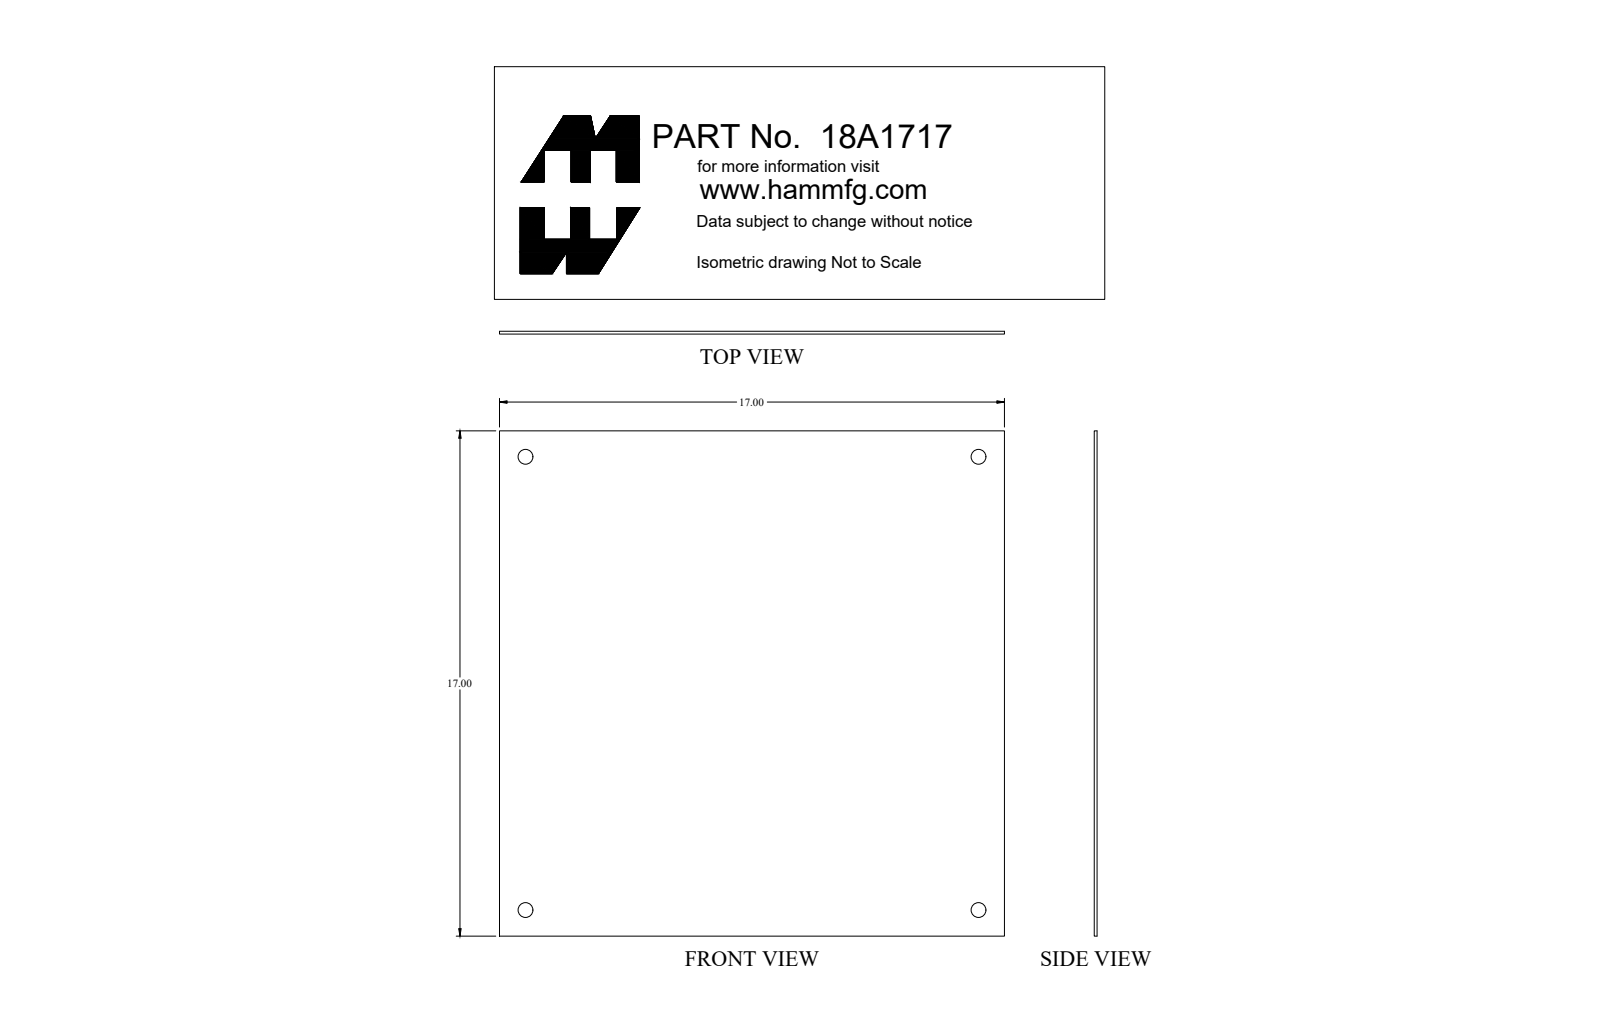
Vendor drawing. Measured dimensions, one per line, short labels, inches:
name: 18A1717
written by: SolidWorks 2018 (AUTOMOTIVE_DESIGN)
unit: in
bodies: 1 solid, 10 faces (6 planar, 4 cylindrical, 0 other)
size: 17 × 17 × 0.095
volume: 27.38 in³; area: 583.5 in²
holes: 4× ⌀0.5
face distances: 0.095, 17
hole spacings: 15.25, 21.567
